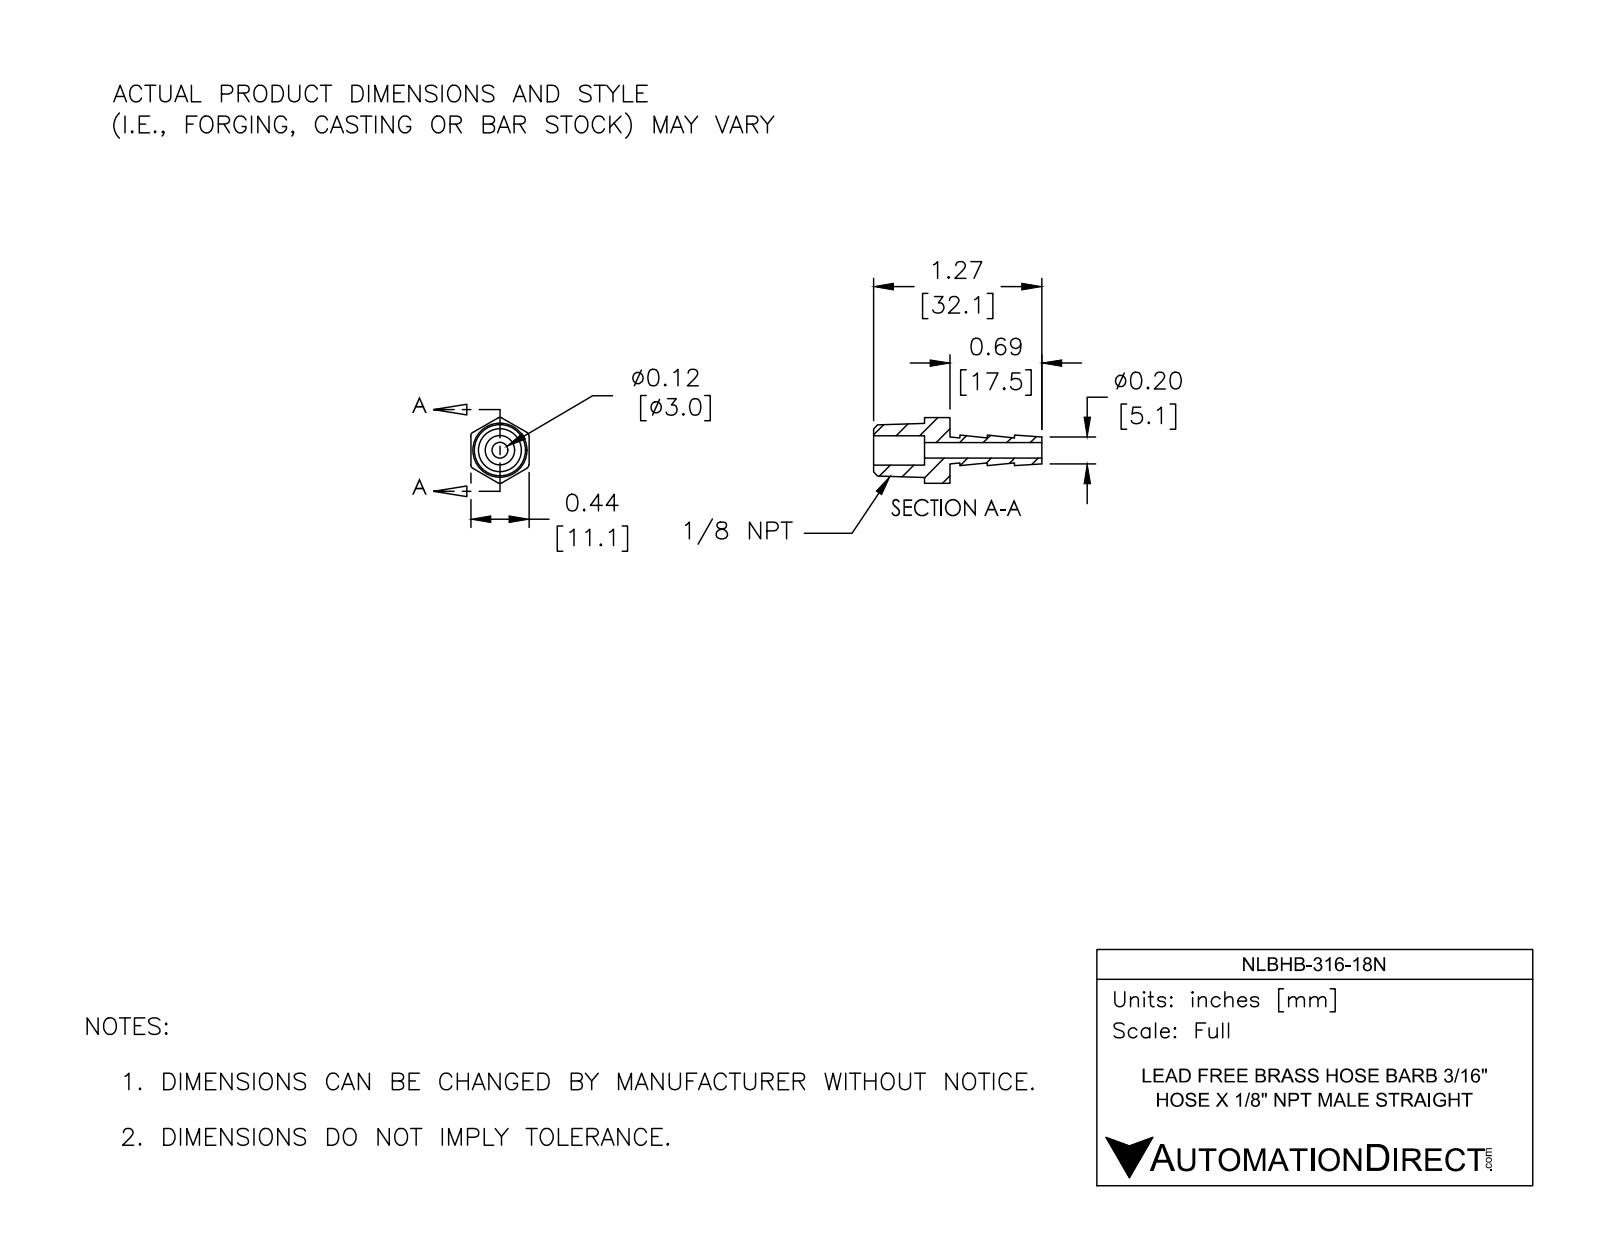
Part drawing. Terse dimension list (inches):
name: NLBHB-316-18N
written by: SolidWorks 2017 (AUTOMOTIVE_DESIGN)
unit: in
bodies: 1 solid, 36 faces (14 planar, 10 cylindrical, 12 other)
size: 1.265 × 0.496 × 0.437
volume: 0.078 in³; area: 2.114 in²
holes: 1× ⌀0.117, 1× ⌀0.22
rounds: 6× R0.03
face distances: 0.438, 0.192, 0.575, 0.383, 0.205, 0.69, 0.882, 1.265, 0.205, 0.41
